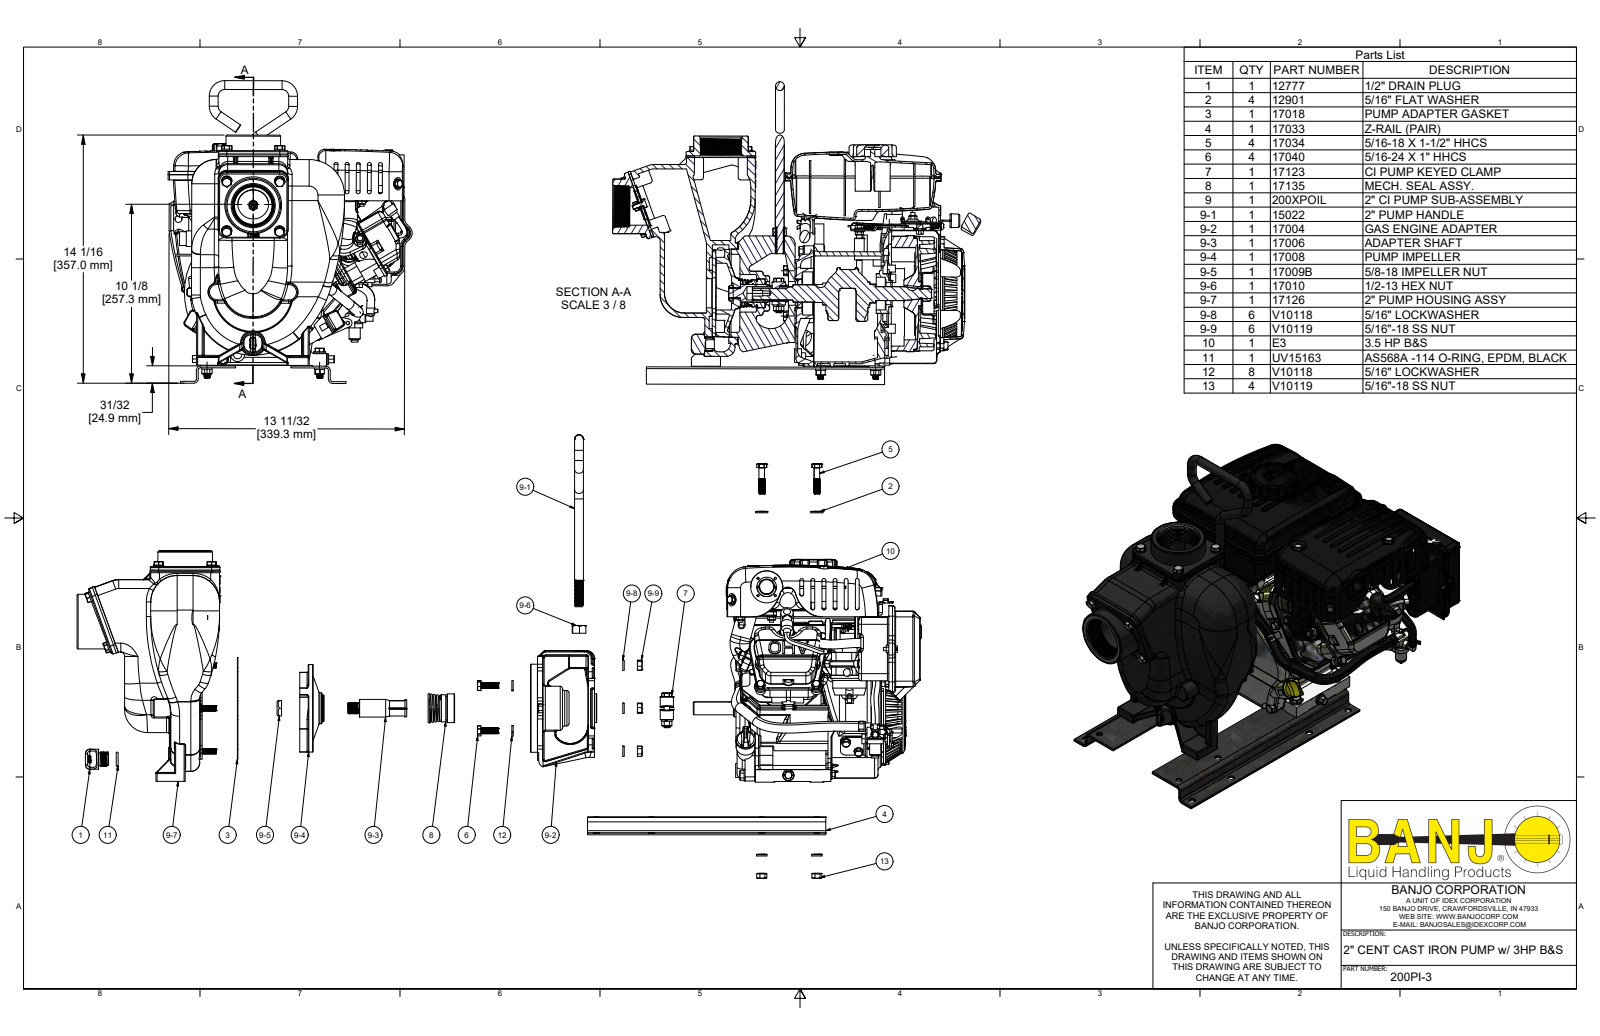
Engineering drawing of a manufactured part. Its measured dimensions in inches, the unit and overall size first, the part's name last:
Units: inches
Overall size (bounding box): 20.848 × 17.15 × 13.835
Round holes (diameter × count): ⌀0.236 ×27, ⌀0.256 ×24, ⌀0.322 ×24, ⌀0.276 ×20, ⌀0.375 ×18, ⌀0.252 ×17, ⌀0.079 ×12, ⌀0.252 ×12, ⌀0.354 ×12, ⌀0.313 ×11, ⌀0.344 ×11, ⌀0.394 ×10
Round bosses / shafts (diameter × count): ⌀0.268 ×222, ⌀0.276 ×92, ⌀0.512 ×37, ⌀0.583 ×24, ⌀0.63 ×23, ⌀0.313 ×20, ⌀0.394 ×16, ⌀0.551 ×15
Partial cylindrical surfaces — rounded edges, fillets, slot ends (radius × count): R0.079 ×345, R0.039 ×333, R0.197 ×189, R0.118 ×135, R0.06 ×131, R0.035 ×90, R0.394 ×88, R0.03 ×80
Main face-to-face distances: 0.105, 0.079, 0.25, 0.031, 0.098, 0.875, 0.028, 0.125, 3.65, 1.584
Hole centre spacings: 3, 2.121, 4.243, 1.661, 0.276, 2.953, 0.138, 0.974
Volume: 407.1 in³ · Surface area: 4 820 in²
Bodies: 242 solids, 18795 faces (5558 planar, 6102 cylindrical, 7135 other)
Part name (STEP PRODUCT): 200PI-3; E3; 4HP_CYLINDER_BLOCK; 4HP_BUSH (+8 more)
STEP written by: Autodesk Inventor 2022 (AUTOMOTIVE_DESIGN)
